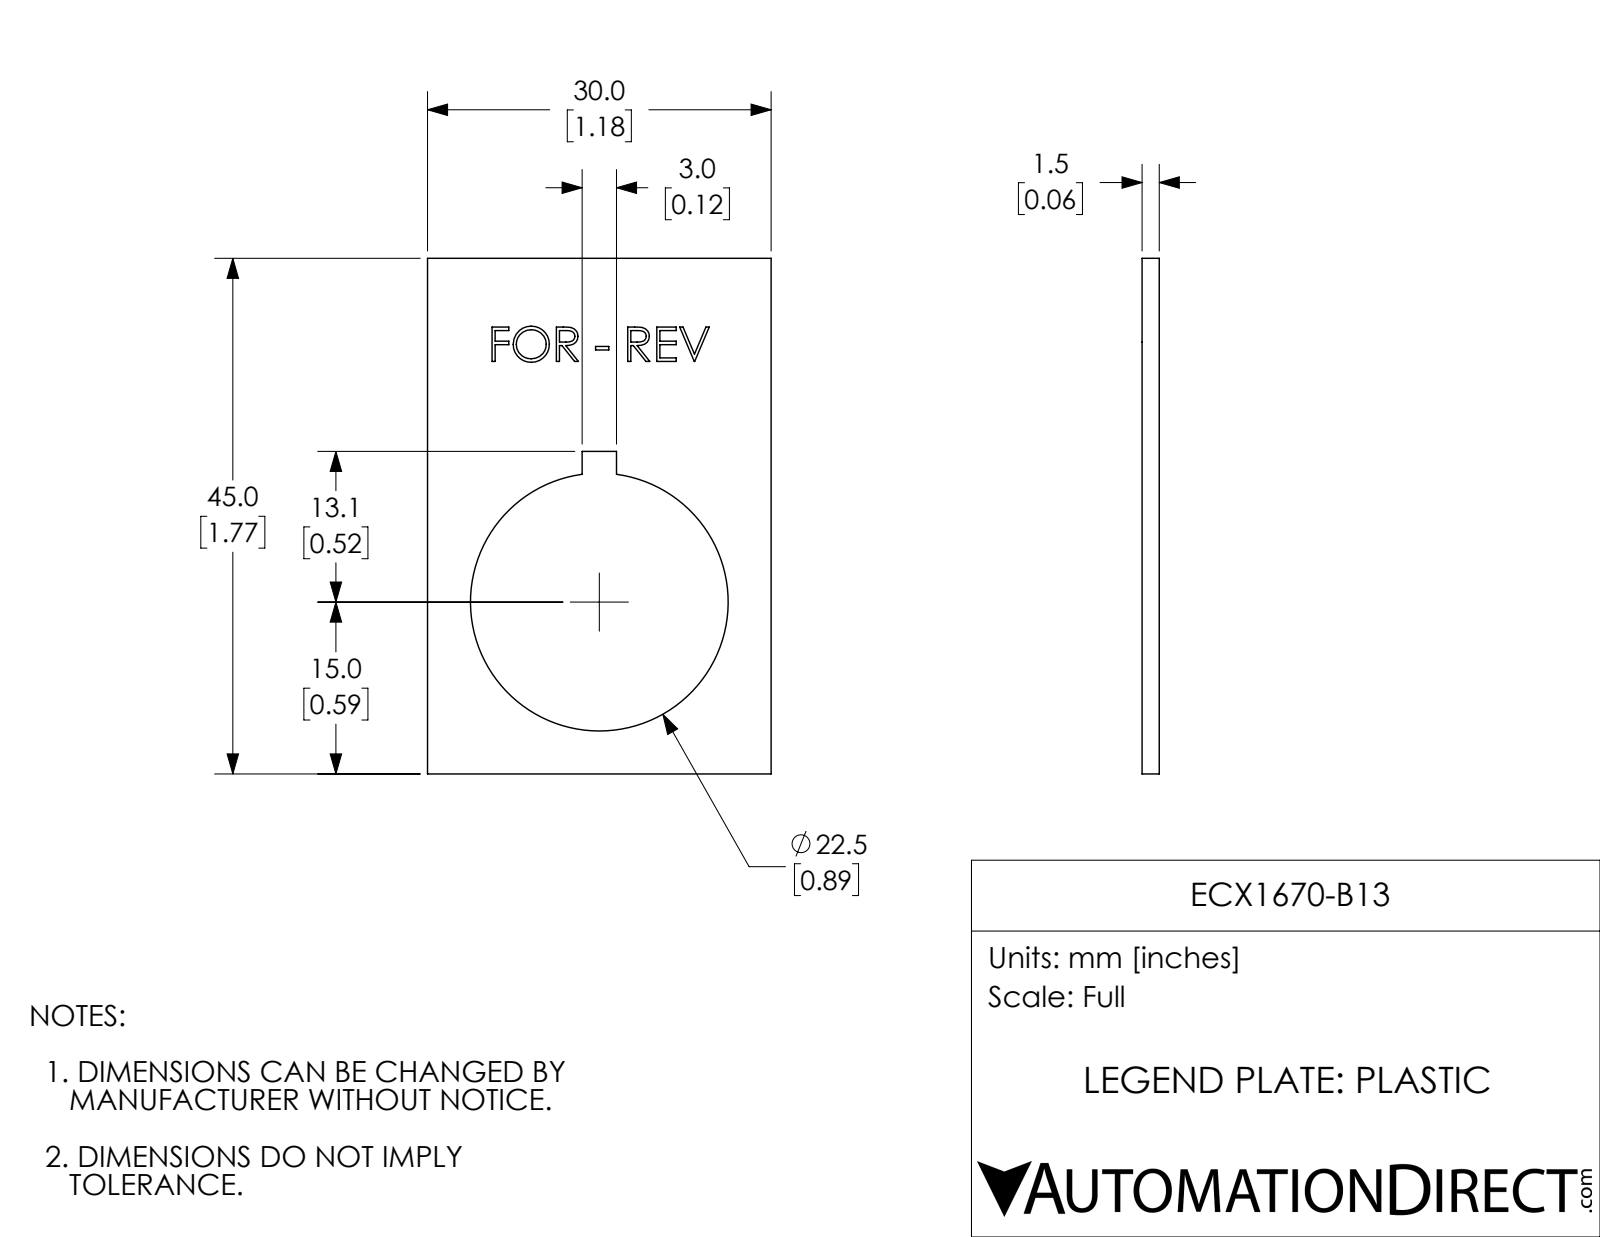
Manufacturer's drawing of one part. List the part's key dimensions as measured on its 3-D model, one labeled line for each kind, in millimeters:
Part name (STEP PRODUCT): ECX1670-B13
STEP written by: SolidWorks 2017 (AUTOMOTIVE_DESIGN)
Units: millimetres
Bodies: 1 solid, 95 faces (74 planar, 3 cylindrical, 18 other)
Overall size (bounding box): 45 × 30 × 1.5
Volume: 1 400 mm³ · Surface area: 2 233 mm²
Round holes (diameter × count): ⌀22.5 ×1
Main face-to-face distances: 1.5, 30, 45, 1.5, 13.5, 16.5, 28.1, 16.8, 3, 0.3
